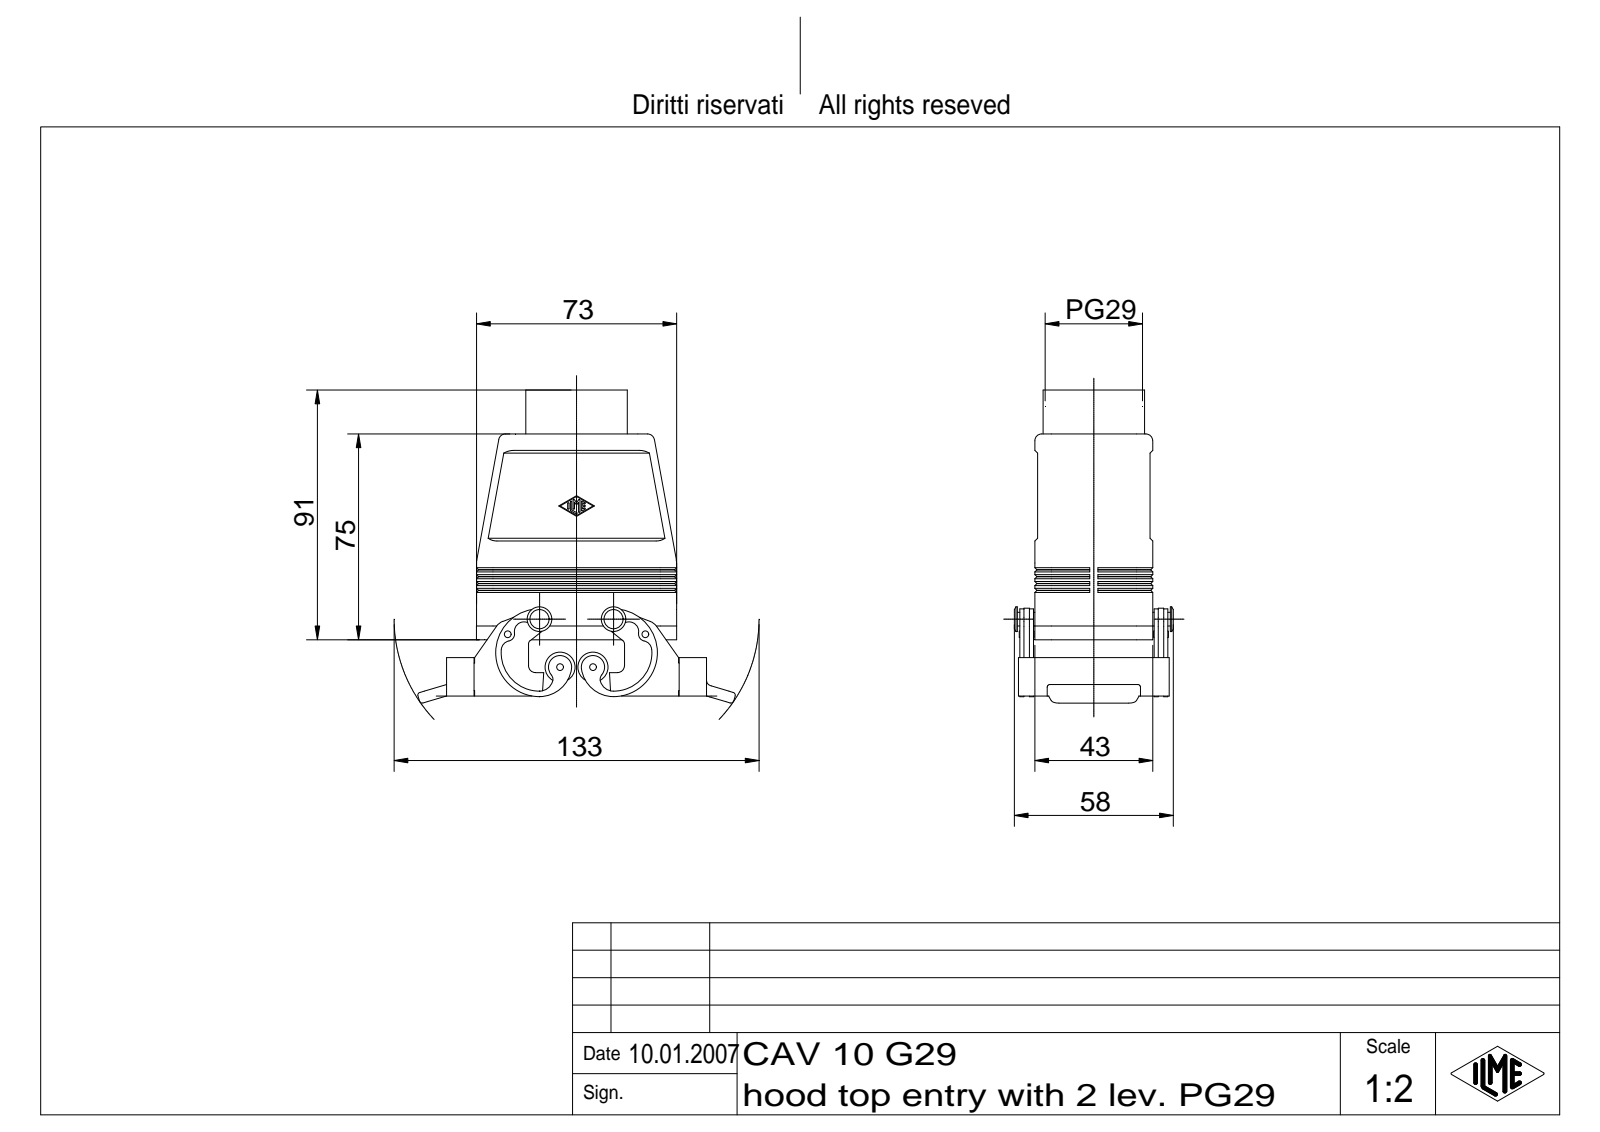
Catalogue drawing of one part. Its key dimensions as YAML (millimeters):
part_name: "CAV Tüllengehäuse 2 Bügel für einen Einsatz"
step_written_by: "Autodesk Inventor 7 (AUTOMOTIVE_DESIGN)"
units: millimeters
bodies: {solids: 1, faces: 850, planar: 259, cylindrical: 230, other: 361}
overall_size: [115.79, 114.08, 58]
volume: 86731
surface_area: 53858
round_holes:
  - {diameter: 2.5, count: 2}
  - {diameter: 33.48, count: 1}
  - {diameter: 35.48, count: 1}
round_bosses_or_shafts:
  - {diameter: 11, count: 2}
  - {diameter: 9, count: 2}
  - {diameter: 5, count: 2}
  - {diameter: 2, count: 2}
  - {diameter: 37, count: 1}
  - {diameter: 34.48, count: 1}
partial_cylinders:
  - {radius: 0.25, count: 14}
  - {radius: 1, count: 12}
  - {radius: 2.5, count: 10}
  - {radius: 6, count: 10}
  - {radius: 3, count: 8}
  - {radius: 2, count: 7}
  - {radius: 3.5, count: 4}
  - {radius: 5, count: 4}
face_to_face_distances: [4, 3, 39, 38, 1, 35, 42, 43, 41, 2]
hole_center_spacings: [50.2]
